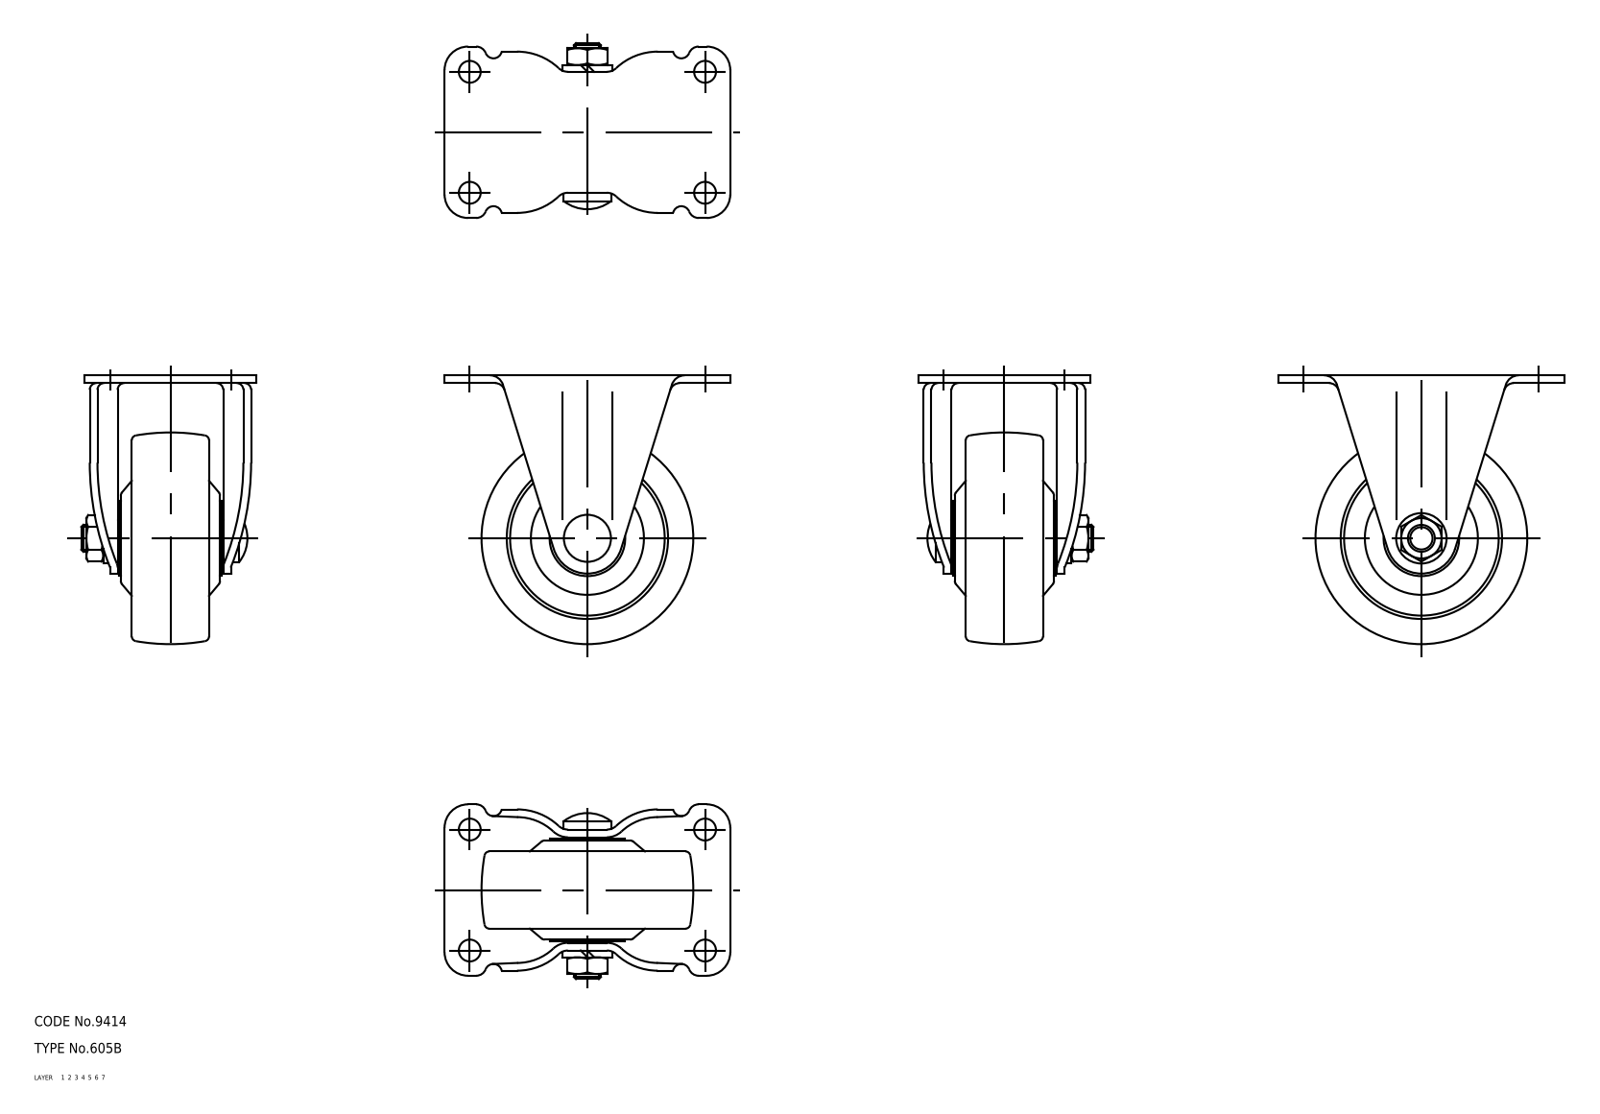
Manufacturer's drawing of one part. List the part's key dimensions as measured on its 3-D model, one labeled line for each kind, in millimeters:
Part name (STEP PRODUCT): 67120681; 67120694; 67120707
STEP written by: CADfix (AUTOMOTIVE_DESIGN)
Units: millimetres
Bodies: 3 solids, 190 faces (0 planar, 0 cylindrical, 190 other)
Overall size (bounding box): 85 × 80 × 52
Volume: 85 370 mm³ · Surface area: 31 564 mm²
